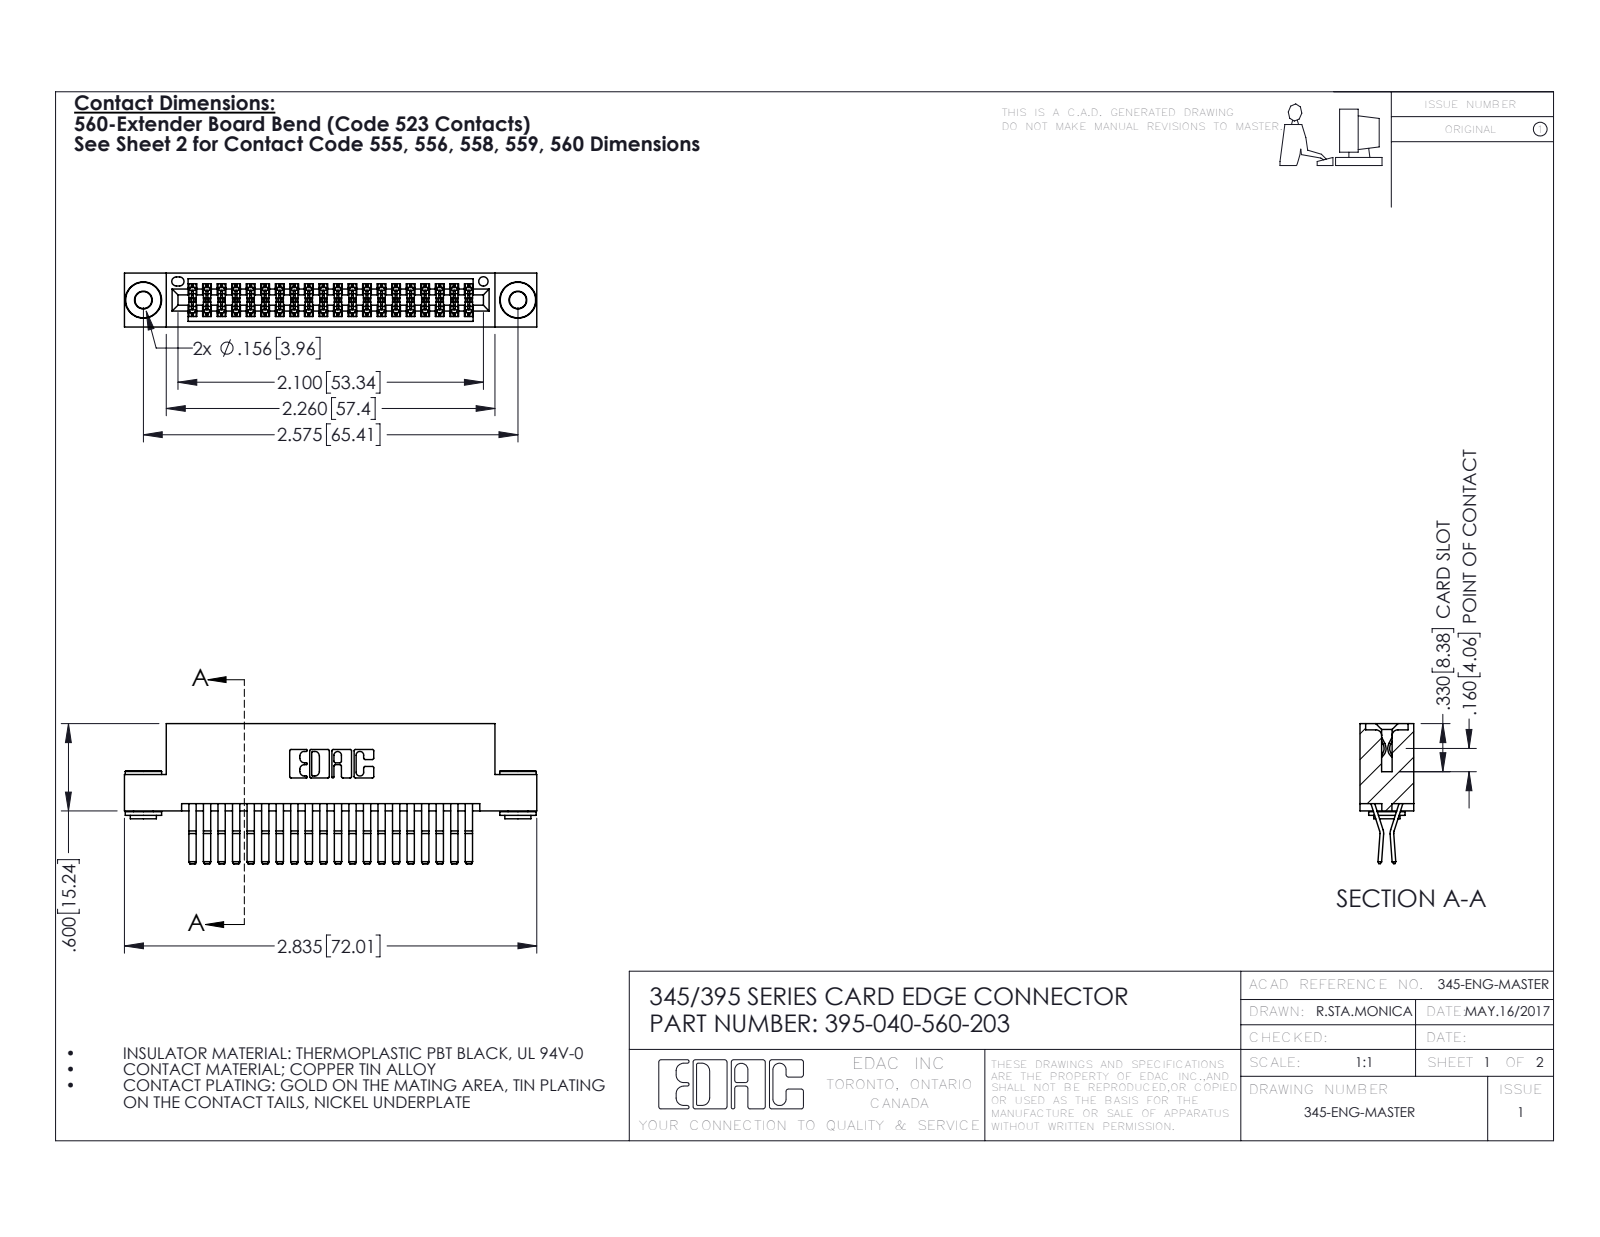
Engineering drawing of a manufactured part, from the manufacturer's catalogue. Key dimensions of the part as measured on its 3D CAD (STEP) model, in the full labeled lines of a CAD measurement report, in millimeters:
Part name (STEP PRODUCT): 345-292-001_560 Tail; 395-040-560-203; 345-250-002_345-250-002-102; 345 Part_Flush Mounting Lugs - 0.156 Dia-TH
STEP written by: SolidWorks 2016 (CONFIG_CONTROL_DESIGN)
Units: millimetres
Bodies: 43 solids, 2244 faces (1410 planar, 826 cylindrical, 8 other)
Overall size (bounding box): 72 × 24.4 × 9.4
Volume: 7 080 mm³ · Surface area: 10 910 mm²
Round holes (diameter × count): ⌀2.9 ×2, ⌀4 ×2, ⌀1.6 ×1
Round bosses / shafts (diameter × count): ⌀6.4 ×2, ⌀4.6 ×2, ⌀3.5 ×2
Partial cylindrical surfaces — rounded edges, fillets, slot ends (radius × count): R0.2 ×60, R0.3 ×22, R0.2 ×6, R0.8 ×6, R0.7 ×3, R0.3 ×2, R0.4 ×2, R0.5 ×2
Main face-to-face distances: 0.6, 1.8, 7.6, 5.1, 9.4, 2.5, 6.9, 5.7, 4.4, 3.8
Hole centre spacings: 6.9, 59.5, 65.4
